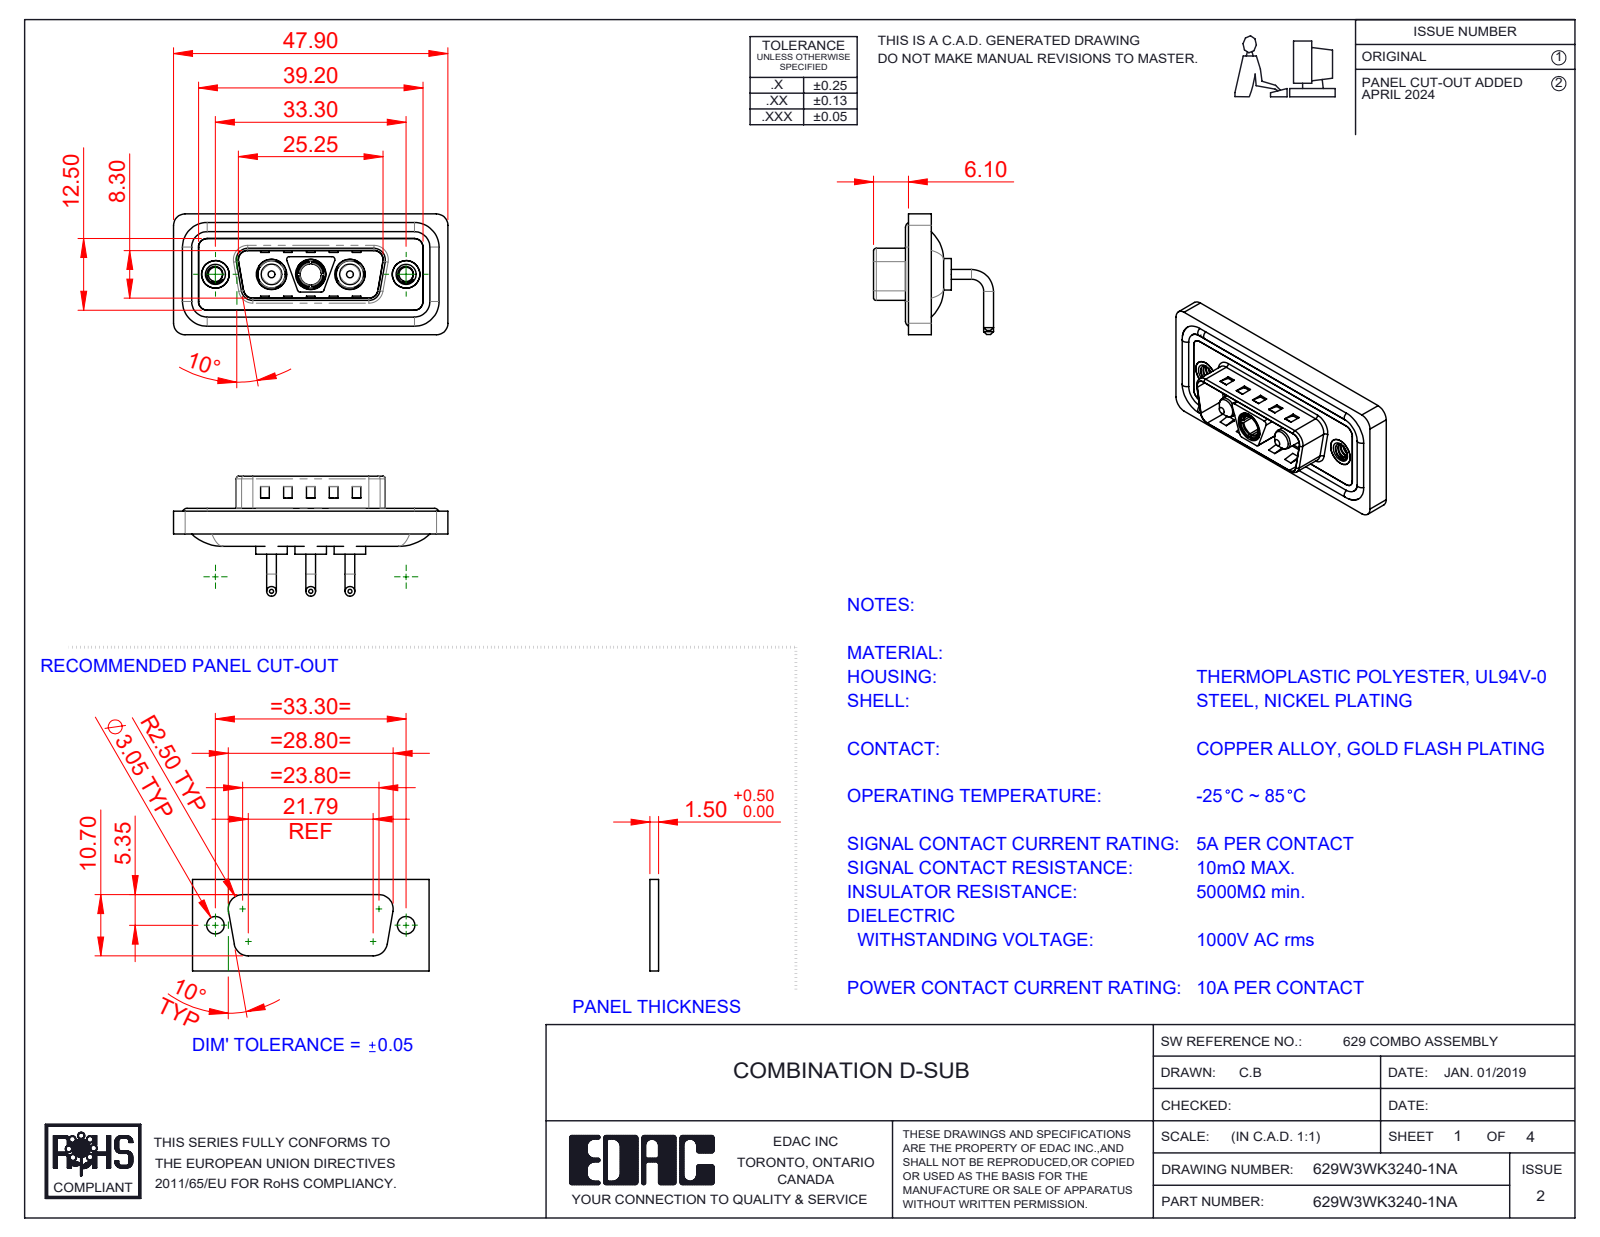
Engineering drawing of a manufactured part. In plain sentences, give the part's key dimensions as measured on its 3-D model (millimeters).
The part is named "629Combo Shell Rear_15 Contacts; 629Combo Waterproof Housing_15 Contacts; 629Combo Shell Front_15 Contacts; 629Combo Threaded Rivet_A (+4 more)". Its 3-D file was written by "SolidWorks 2023 (CONFIG_CONTROL_DESIGN)". It is 13 solids with 615 faces: 231 planar, 254 cylindrical and 130 other. Overall it measures 47.9 by 21.1 by 20.95 millimeters. Its volume is 5 712 cubic millimeters and its surface area 9 264 square millimeters. Round holes: 3 of diameter 4.85, 3 of diameter 5.3, 2 of diameter 2.5, 2 of diameter 4, 2 of diameter 4.8, 2 of diameter 5, 1 of diameter 3.7. Round bosses or shafts: 6 of diameter 1.7, 4 of diameter 1.6, 3 of diameter 5.5, 3 of diameter 5.2, 3 of diameter 4.75, 3 of diameter 3.75, 2 of diameter 4.9, 2 of diameter 3.6. Partial cylindrical surfaces (rounded edges, fillets, slot ends): 20 of radius 2, 18 of radius 1.5, 12 of radius 0.5, 8 of radius 1.6, 4 of radius 0.25, 4 of radius 0.6, 4 of radius 0.65, 4 of radius 0.9. The main face-to-face distances are 0.4, 2.9, 0.8, 1.1, 2.1, 1.6, 4.5, 3.1, 2.5, 1.5. The hole center spacings are 6.85, 9.8, 16.65, 23.5, 13.7, 33.3.
